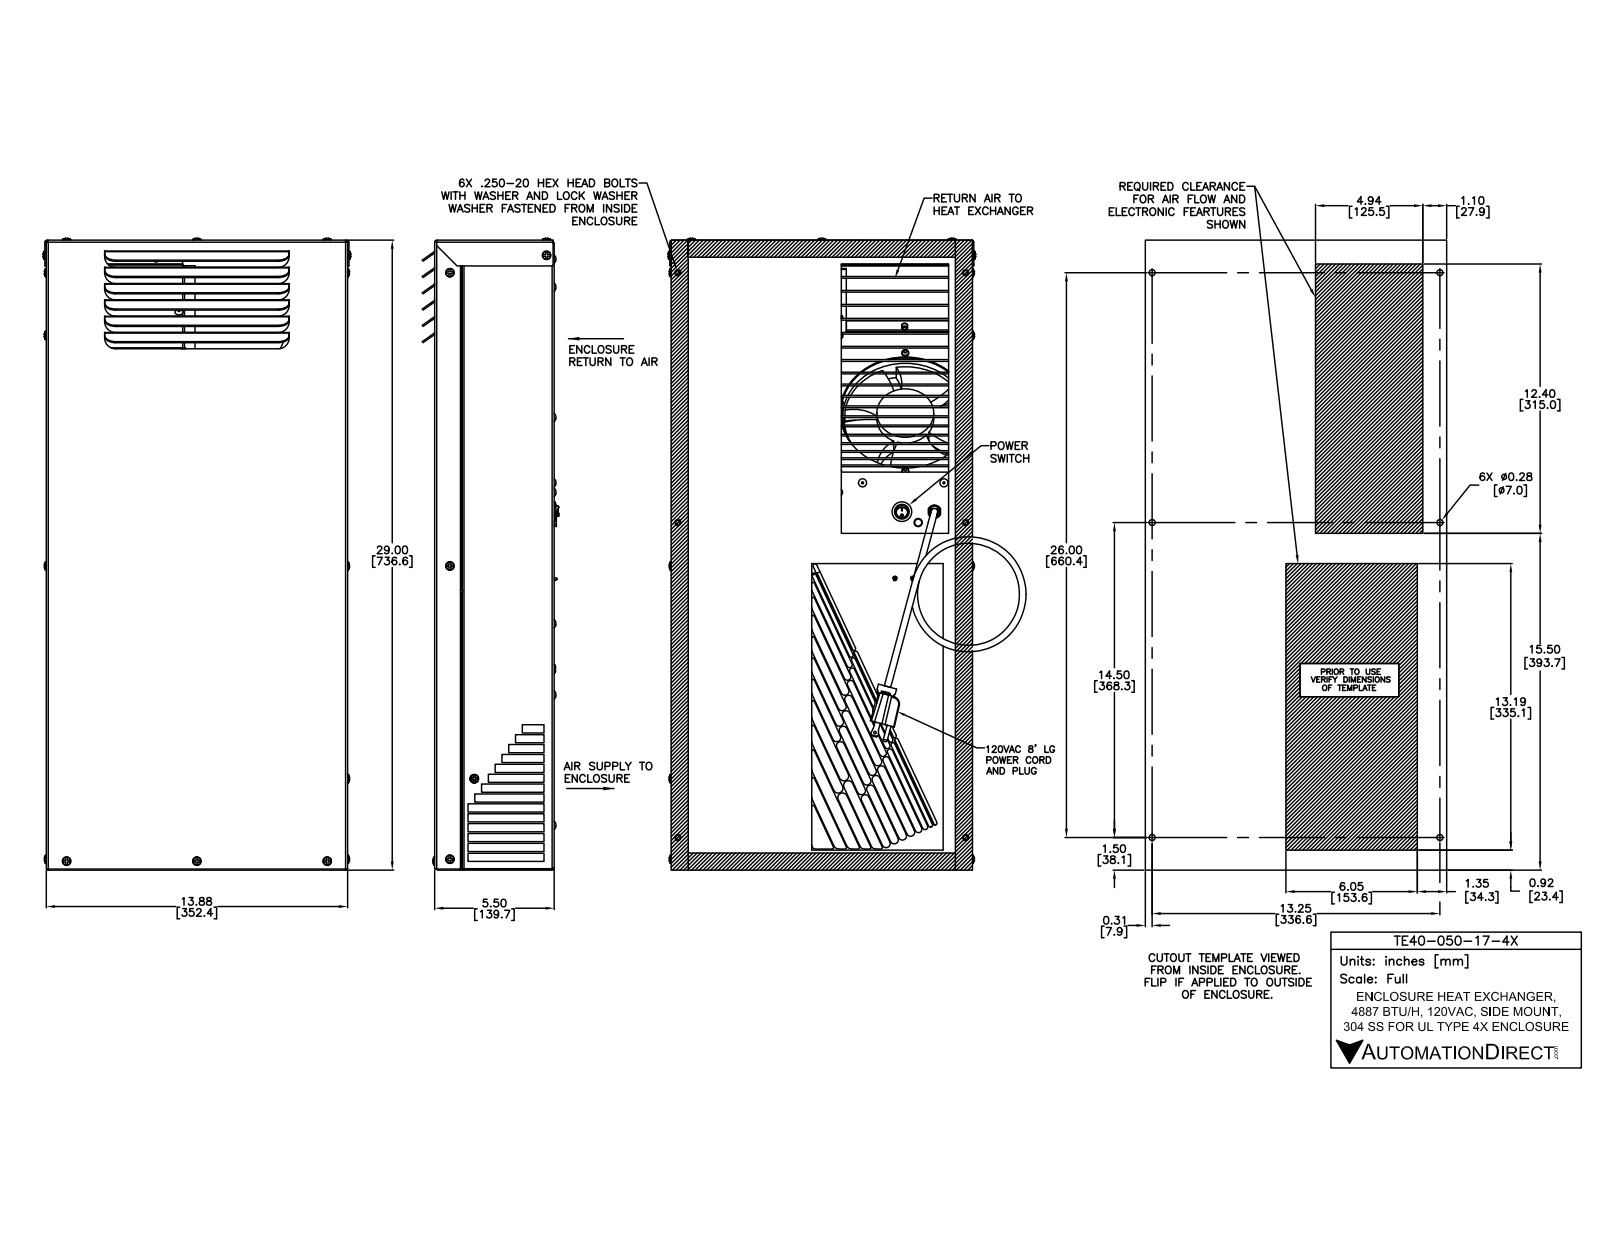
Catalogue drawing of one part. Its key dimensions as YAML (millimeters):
part_name: "TE40-050-17-4X"
step_written_by: "SolidWorks 2017 (AUTOMOTIVE_DESIGN)"
units: millimeters
bodies: {solids: 125, faces: 3479, planar: 1943, cylindrical: 1134, other: 402}
overall_size: [739, 419.1, 241.5]
volume: 5545000
surface_area: 3398000
round_holes:
  - {diameter: 4.9, count: 21}
  - {diameter: 5.6, count: 17}
  - {diameter: 4.8, count: 15}
  - {diameter: 4, count: 14}
  - {diameter: 5.2, count: 11}
  - {diameter: 13.1, count: 9}
  - {diameter: 2.8, count: 8}
  - {diameter: 4.4, count: 8}
  - {diameter: 12.7, count: 8}
  - {diameter: 22.5, count: 8}
  - {diameter: 5.1, count: 6}
  - {diameter: 6.9, count: 6}
round_bosses_or_shafts:
  - {diameter: 6.9, count: 15}
  - {diameter: 4.8, count: 14}
  - {diameter: 25.4, count: 8}
  - {diameter: 23.7, count: 8}
  - {diameter: 14.3, count: 6}
  - {diameter: 8.3, count: 6}
  - {diameter: 8.3, count: 6}
  - {diameter: 6.3, count: 6}
partial_cylinders:
  - {radius: 0.3, count: 96}
  - {radius: 0.4, count: 96}
  - {radius: 0.8, count: 46}
  - {radius: 2.4, count: 46}
  - {radius: 1.5, count: 28}
  - {radius: 1.2, count: 24}
  - {radius: 4.8, count: 19}
  - {radius: 1.6, count: 17}
face_to_face_distances: [1.6, 1.6, 139.7, 138.1, 136.6, 138.1, 350.9, 6.4, 158.8, 192.1]
hole_center_spacings: [31.8, 63.5, 95.3, 81, 81, 81, 73.6, 162]
